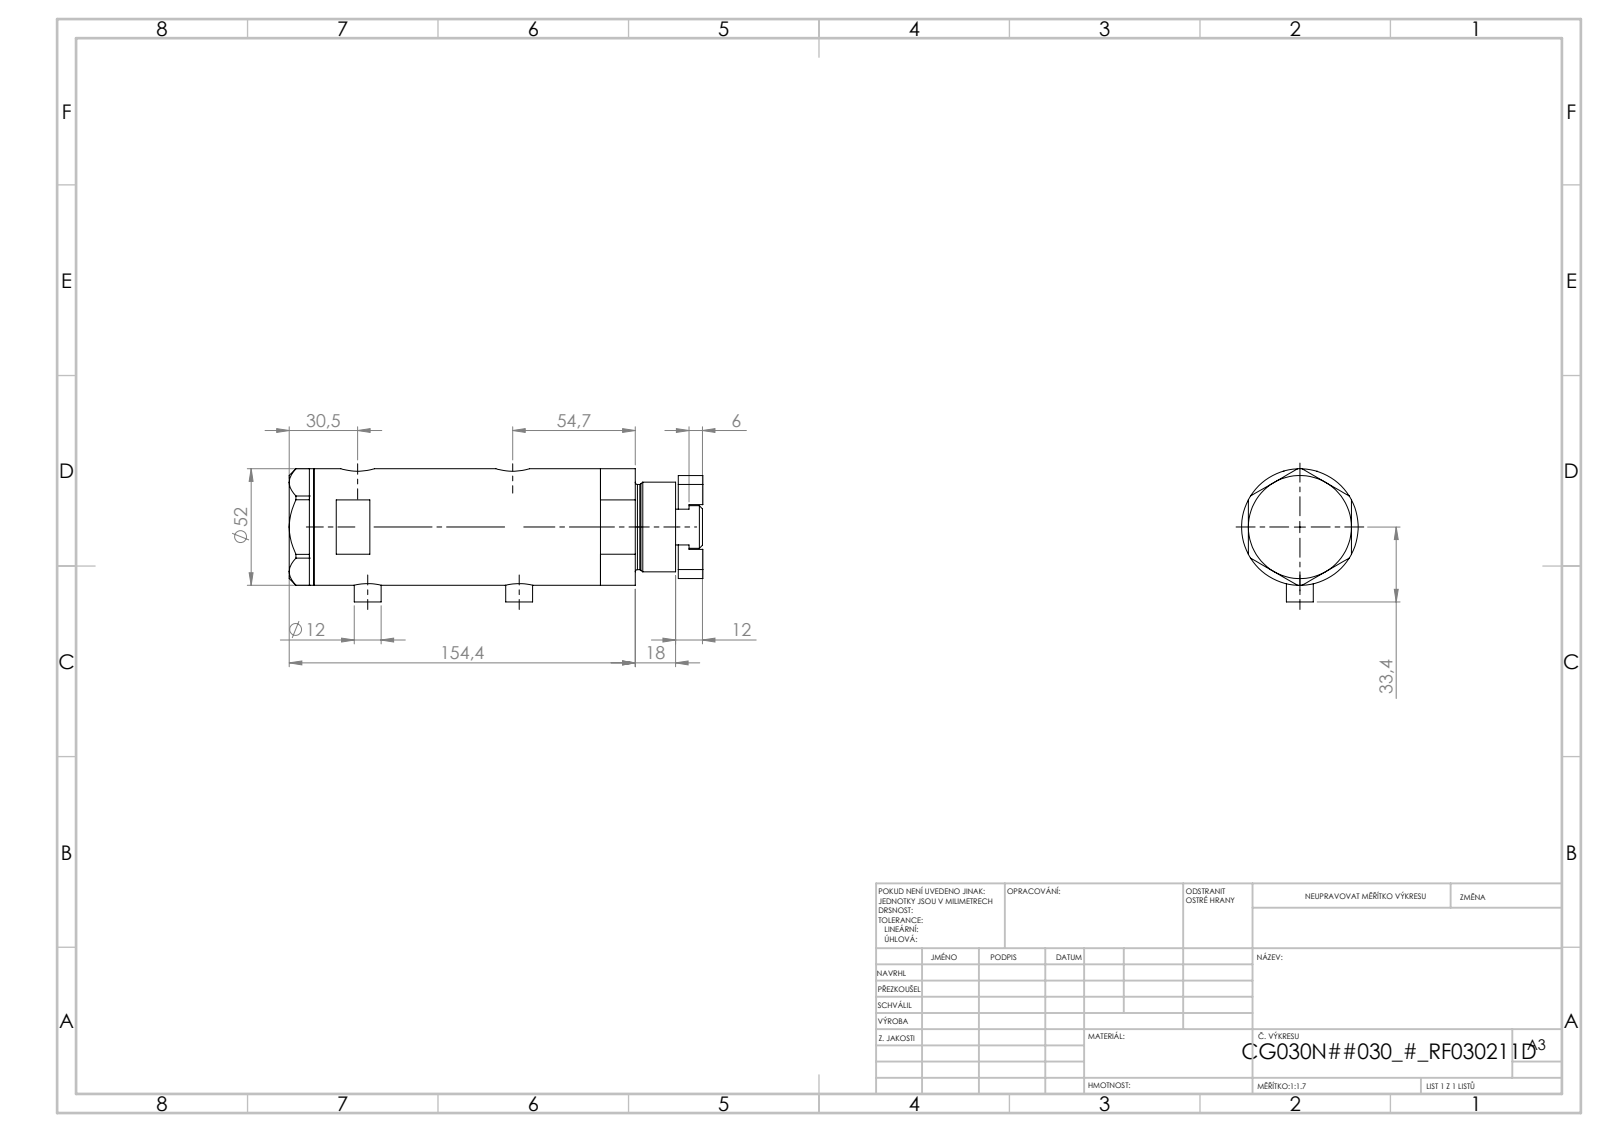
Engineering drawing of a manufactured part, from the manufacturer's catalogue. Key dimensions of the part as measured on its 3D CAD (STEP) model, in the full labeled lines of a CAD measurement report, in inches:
Part name (STEP PRODUCT): V270CG_VC; V270CG_MIDDLE; V270CG_FRONT; V270CG_BACK (+1 more)
STEP written by: SolidWorks 2019 (CONFIG_CONTROL_DESIGN)
Units: inches
Bodies: 6 solids, 174 faces (89 planar, 65 cylindrical, 20 other)
Overall size (bounding box): 7.268 × 2.339 × 2.047
Volume: 20.7 in³ · Surface area: 124.9 in²
Round holes (diameter × count): ⌀0.201 ×4, ⌀0.354 ×4, ⌀0.383 ×2, ⌀0.492 ×2, ⌀0.591 ×2, ⌀0.256 ×1, ⌀0.787 ×1, ⌀0.846 ×1, ⌀1.181 ×1, ⌀1.299 ×1, ⌀1.732 ×1
Round bosses / shafts (diameter × count): ⌀0.472 ×2, ⌀2.047 ×1, ⌀1.575 ×1, ⌀1.496 ×1, ⌀0.748 ×1
Main face-to-face distances: 0.433, 3.602, 0.937, 2.665, 1.37, 4.035, 1.811, 1.319, 5.469, 5.035
Hole centre spacings: 0.659, 0.394, 1.258, 1.319, 0.114, 0.177, 2.547, 2.661
